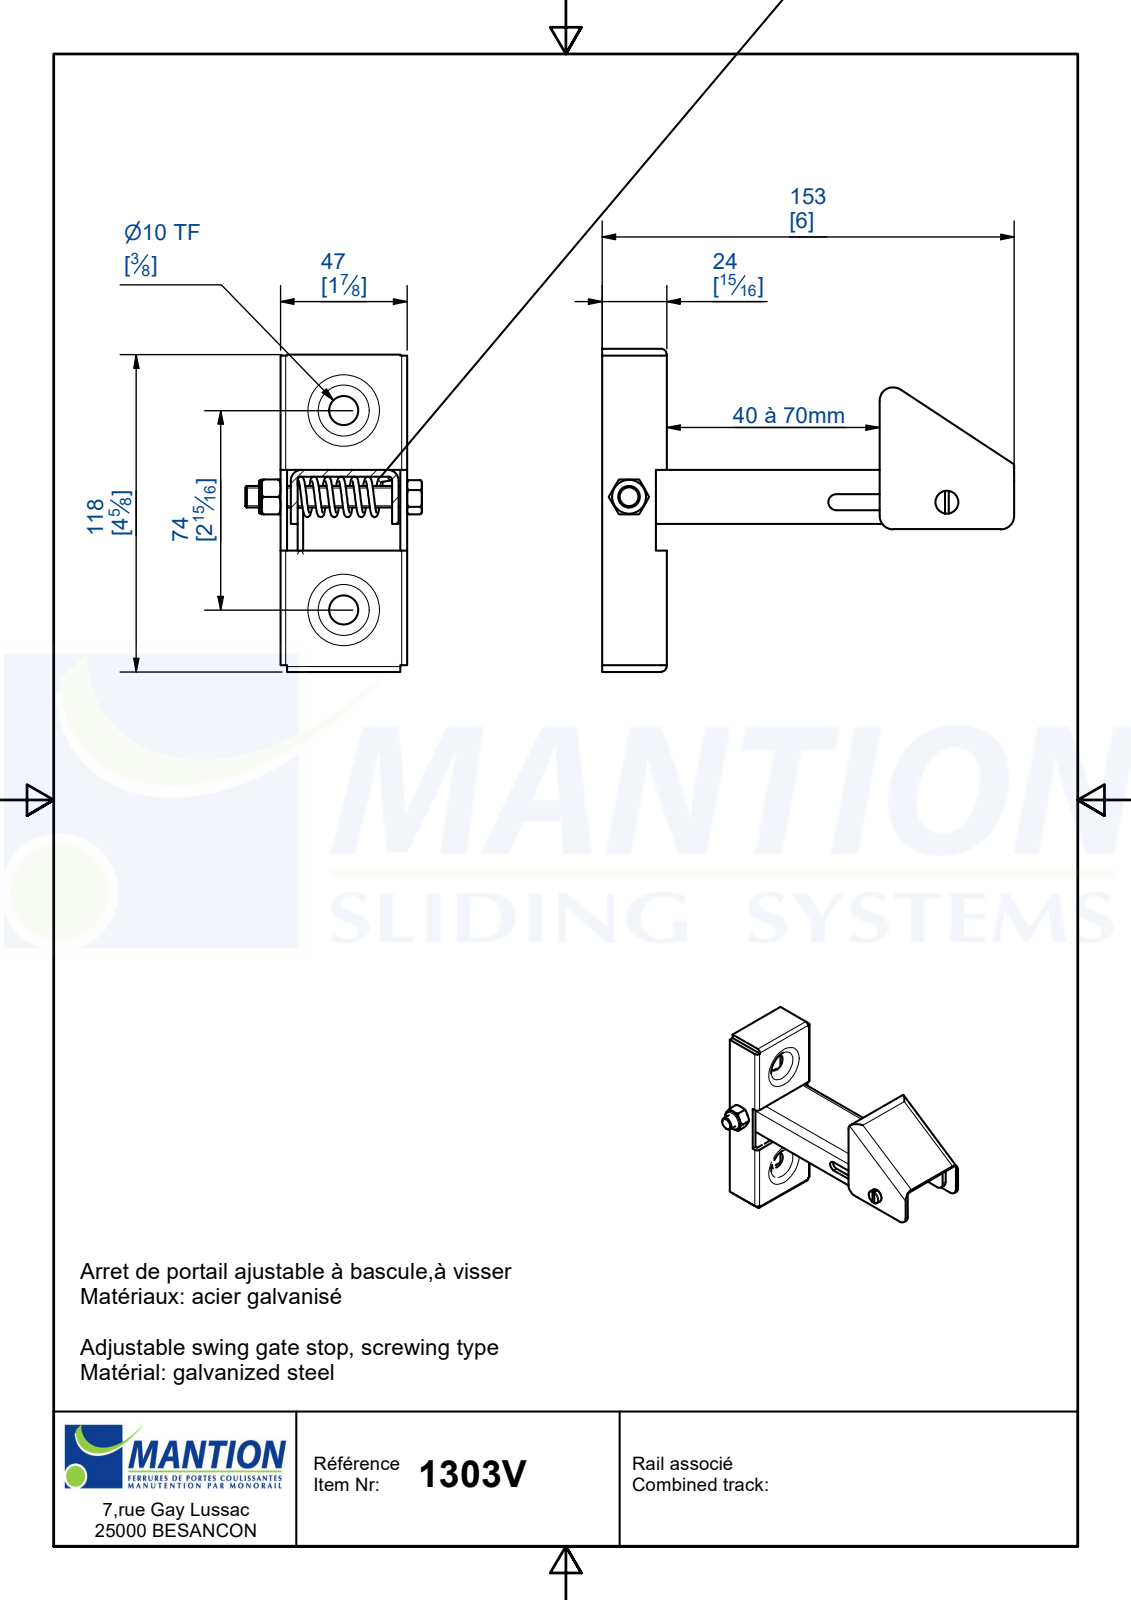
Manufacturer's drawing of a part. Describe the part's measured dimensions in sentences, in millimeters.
The part is named "Pièce1". Its 3-D file was written by "Autodesk Inventor 2017 (AUTOMOTIVE_DESIGN)". It is 1 solid with 205 faces: 114 planar, 49 cylindrical and 42 other. Overall it measures 153 by 120 by 65.5 millimeters. Its volume is 71 787 cubic millimeters and its surface area 65 629 square millimeters. Round holes: 1 of diameter 4.13, 1 of diameter 5.1, 1 of diameter 6.65, 1 of diameter 8.2. Round bosses or shafts: 3 of diameter 2, 1 of diameter 12.5, 1 of diameter 8, 1 of diameter 5, 1 of diameter 4.51. Partial cylindrical surfaces (rounded edges, fillets, slot ends): 7 of radius 5, 5 of radius 3, 4 of radius 2, 2 of radius 1, 2 of radius 4. The main face-to-face distances are 2.5, 2, 44.5, 42, 3.89, 40.61, 41.39, 3.11, 37.5, 5.5. The hole center spacings are 118.02.
